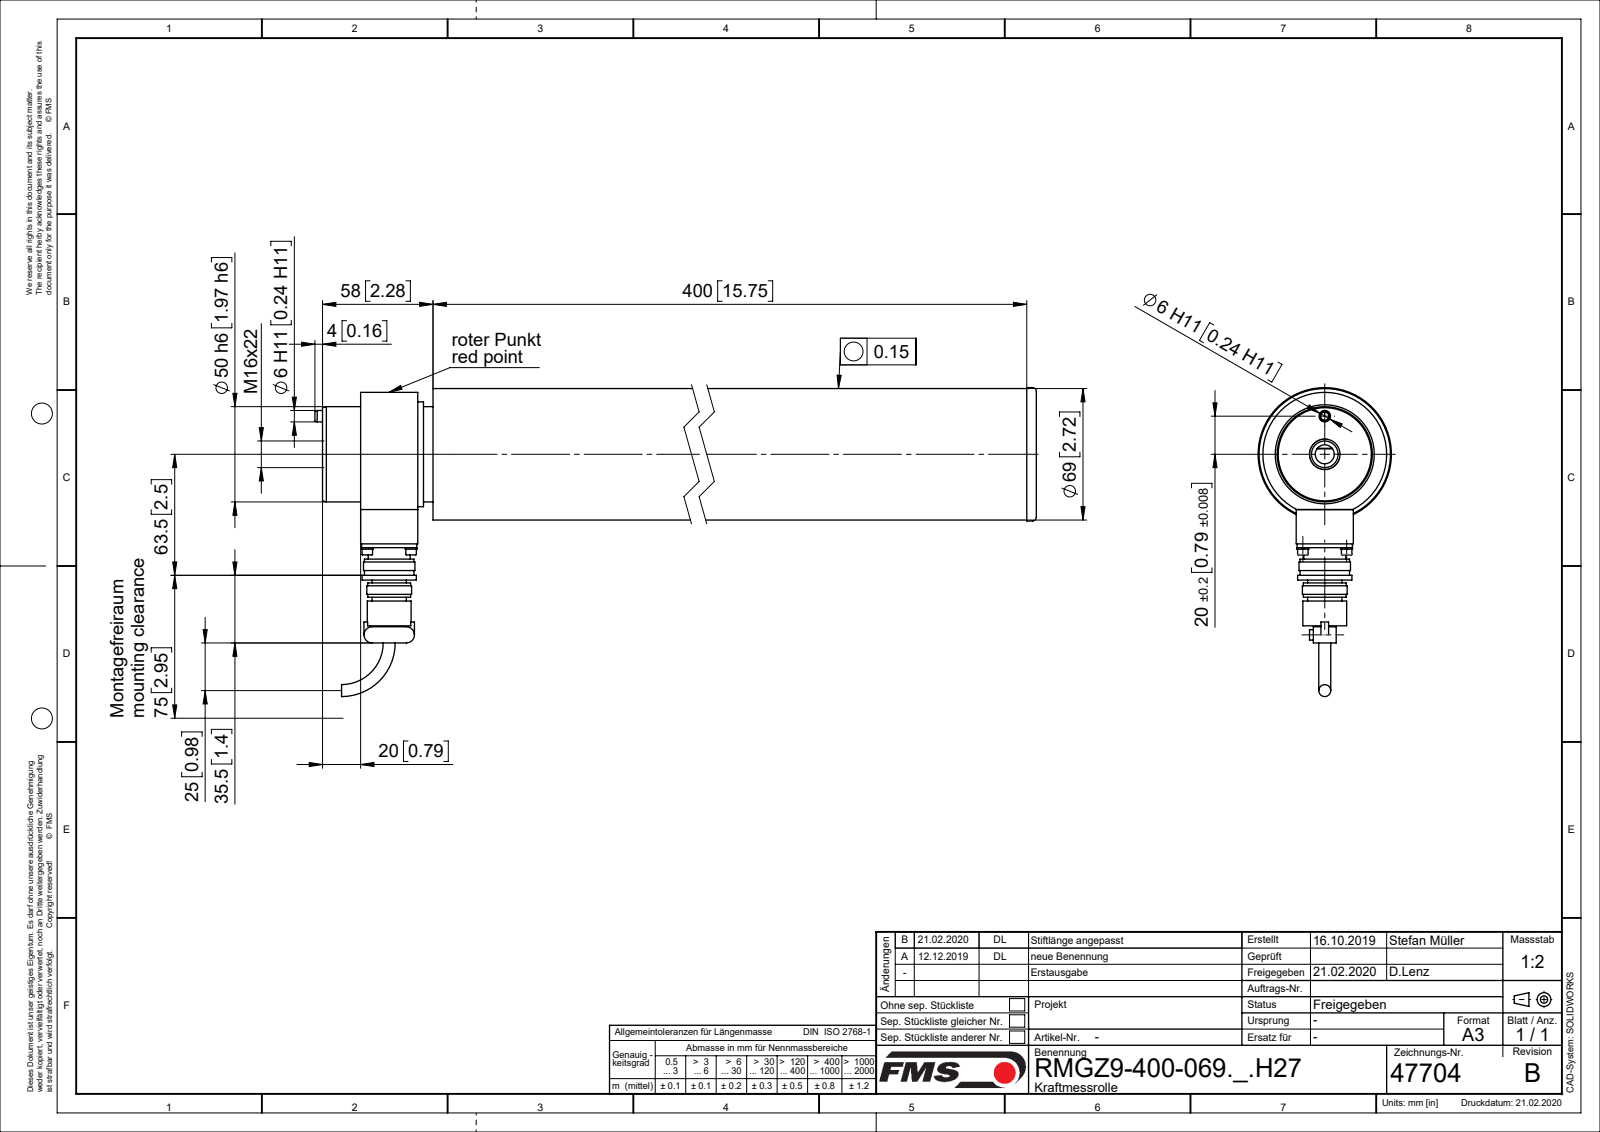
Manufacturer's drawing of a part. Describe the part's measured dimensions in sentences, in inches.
The part is named "Zyl-Schr DIN912_M3x25; Spannstift_ISO13337_D06x12; 47679_01; 47704_stp (+8 more)". Its 3-D file was written by "SolidWorks 2018 (CONFIG_CONTROL_DESIGN)". It is 31 solids with 597 faces: 172 planar, 259 cylindrical and 166 other. Overall it measures 18.386 by 6.384 by 2.756 inches. Its volume is 52.1 cubic inches and its surface area 474.2 square inches. Round holes: 6 of diameter 0.098, 4 of diameter 0.122, 4 of diameter 0.134, 1 of diameter 0.13, 1 of diameter 0.197, 1 of diameter 0.236, 1 of diameter 0.394, 1 of diameter 0.472, 1 of diameter 0.551, 1 of diameter 0.669, 1 of diameter 0.866, 1 of diameter 0.906. Round bosses or shafts: 6 of diameter 0.217, 4 of diameter 0.244, 4 of diameter 0.118, 4 of diameter 0.098, 1 of diameter 2.756, 1 of diameter 2.717, 1 of diameter 2.559, 1 of diameter 2.283. Partial cylindrical surfaces (rounded edges, fillets, slot ends): 4 of radius 0.004, 4 of radius 0.433, 2 of radius 0.165, 2 of radius 0.167, 1 of radius 0.689, 1 of radius 0.874, 1 of radius 0.999. The main face-to-face distances are 1.969, 0.118, 1.378, 0.079, 0.197, 5.236, 16.063, 0.787, 10.827, 5.591. The hole center spacings are 0.64, 0.906, 0.978, 1.281, 0.714, 0.787, 1.007, 1.463.
